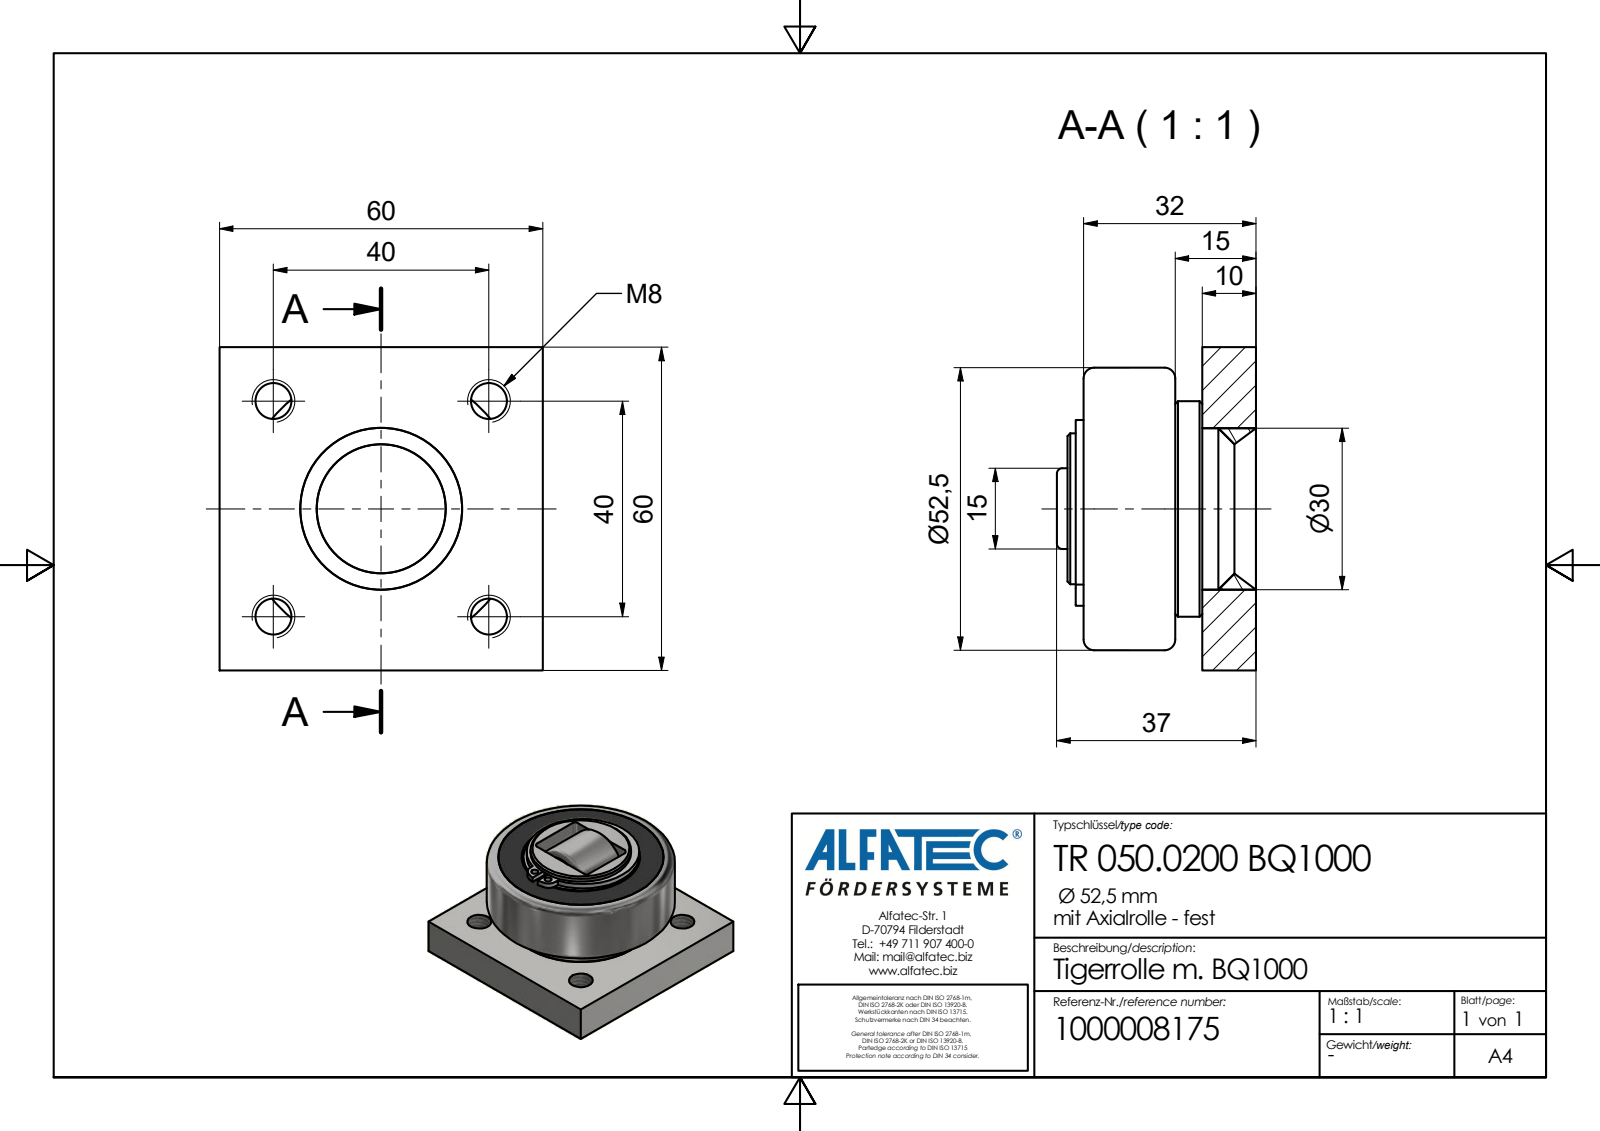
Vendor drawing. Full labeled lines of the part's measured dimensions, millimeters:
Part name (STEP PRODUCT): TR 050.0200 BQ1000_Kontur
STEP written by: Autodesk Inventor 2020 (AP242_MANAGED_MODEL_BASED_3D_ENGINEERING_MIM_LF)
Units: millimetres
Bodies: 1 solid, 383 faces (222 planar, 149 cylindrical, 12 other)
Overall size (bounding box): 60 × 60 × 37
Volume: 73 378 mm³ · Surface area: 28 145 mm²
Round holes (diameter × count): ⌀6.65 ×4, ⌀2 ×2, ⌀10.5 ×1, ⌀28 ×1, ⌀38 ×1, ⌀41 ×1, ⌀46 ×1
Round bosses / shafts (diameter × count): ⌀4 ×29, ⌀40 ×1, ⌀36 ×1, ⌀33 ×1, ⌀32 ×1, ⌀31.37 ×1, ⌀26.6 ×1, ⌀9.5 ×1
Partial cylindrical surfaces — rounded edges, fillets, slot ends (radius × count): R1 ×4, R3 ×2, R10.25 ×1
Main face-to-face distances: 10, 1.6, 15.4, 60, 32, 22, 2.3, 14.7, 0.7, 13.1
Hole centre spacings: 28.28, 40, 15.75, 17.96, 23.04, 39.56, 42.11, 56.57
